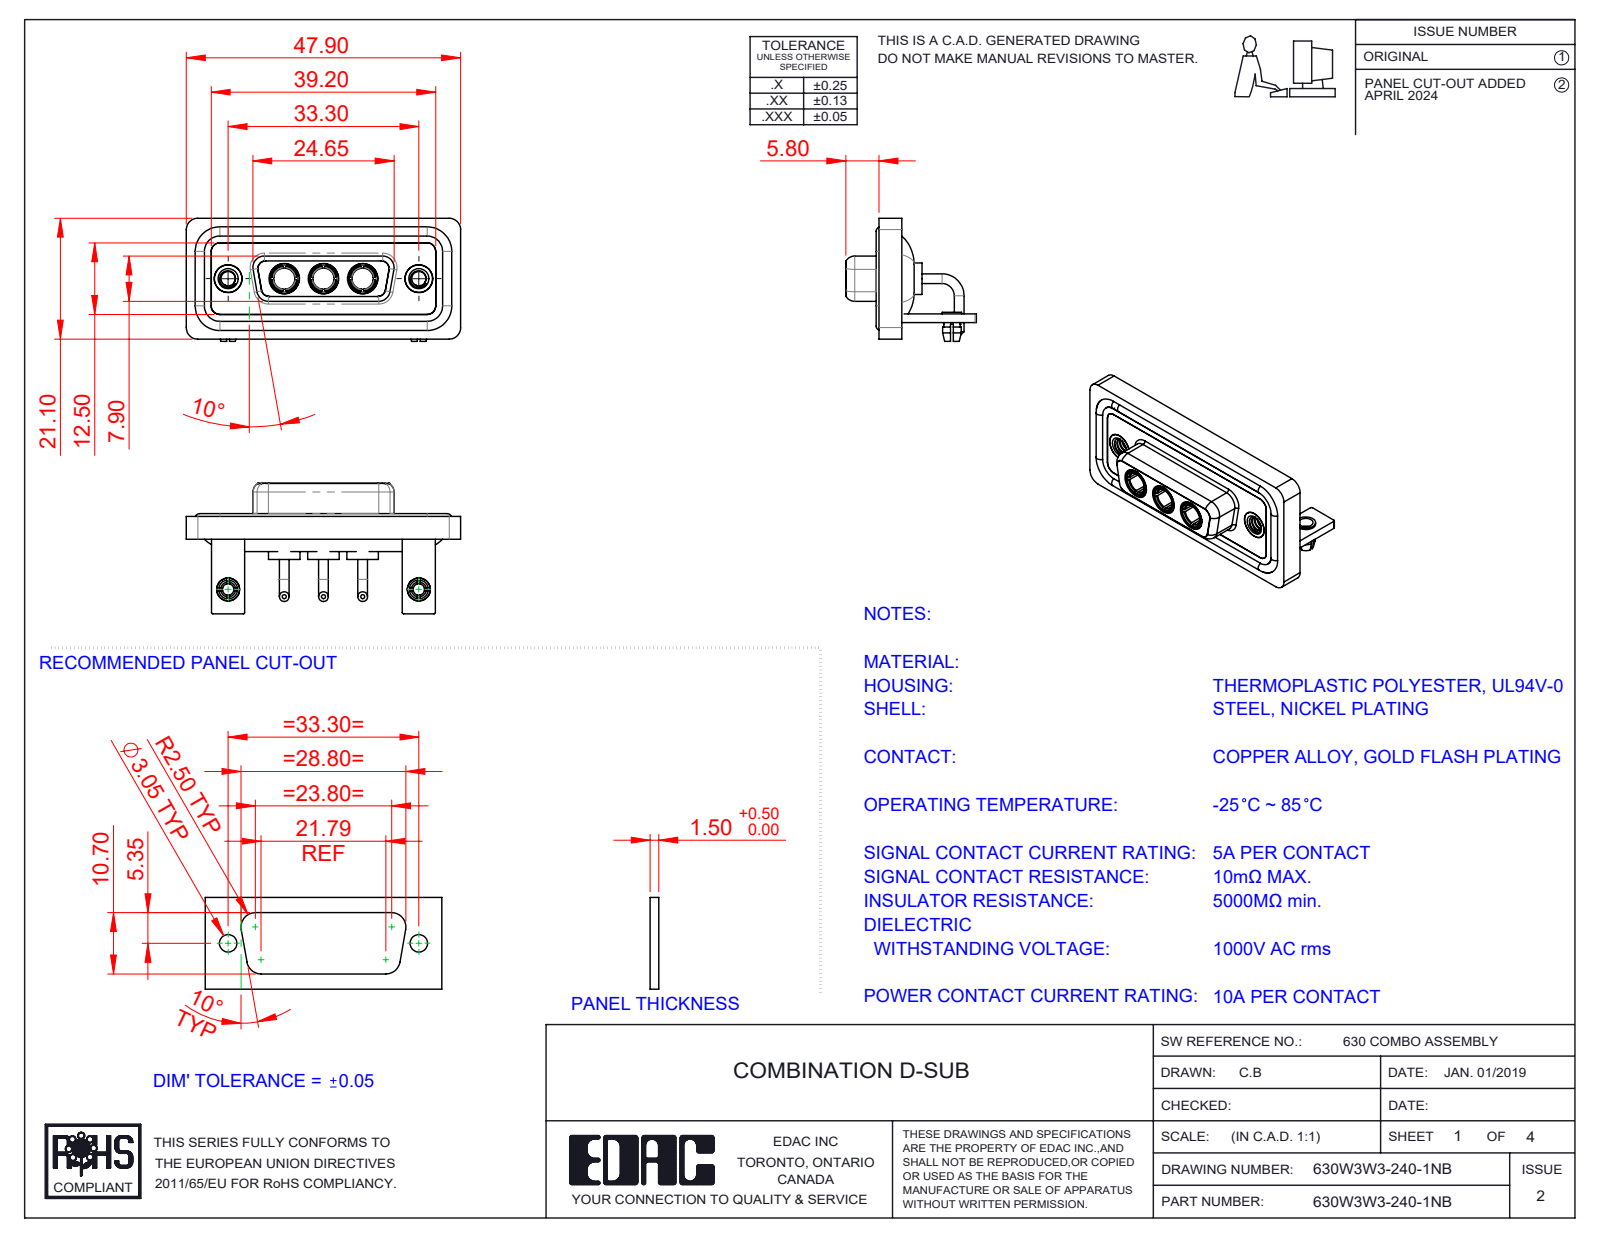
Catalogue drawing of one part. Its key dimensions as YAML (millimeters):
part_name: "630Combo Housing_3W3; 630Combo Shell Front_15 Contacts; 630W3W3-140-1NB; 630Combo Stabilizer Bracket_50 Contacts (+5 more)"
step_written_by: "SolidWorks 2023 (CONFIG_CONTROL_DESIGN)"
units: millimeters
bodies: {solids: 17, faces: 754, planar: 260, cylindrical: 317, other: 177}
overall_size: [47.9, 22.8, 21.5]
volume: 6402
surface_area: 10769
round_holes:
  - {diameter: 4.85, count: 5}
  - {diameter: 2.5, count: 4}
  - {diameter: 3.7, count: 3}
  - {diameter: 5.3, count: 3}
  - {diameter: 2, count: 2}
  - {diameter: 3.2, count: 2}
  - {diameter: 4, count: 2}
  - {diameter: 4.05, count: 2}
  - {diameter: 5, count: 2}
round_bosses_or_shafts:
  - {diameter: 1.7, count: 6}
  - {diameter: 1.6, count: 4}
  - {diameter: 5.5, count: 3}
  - {diameter: 5.2, count: 3}
  - {diameter: 4.96, count: 3}
  - {diameter: 4.75, count: 3}
  - {diameter: 3.75, count: 3}
  - {diameter: 4.95, count: 2}
partial_cylinders:
  - {radius: 2, count: 21}
  - {radius: 1.5, count: 18}
  - {radius: 0.25, count: 16}
  - {radius: 1.35, count: 12}
  - {radius: 1.6, count: 8}
  - {radius: 0.5, count: 5}
  - {radius: 0.6, count: 4}
  - {radius: 0.65, count: 4}
face_to_face_distances: [0.4, 2.9, 1.5, 1.8, 3.7, 1.1, 4.1, 1.6, 2.5, 1.4]
hole_center_spacings: [6.85, 9.8, 16.65, 23.5, 33.3, 13.7]
